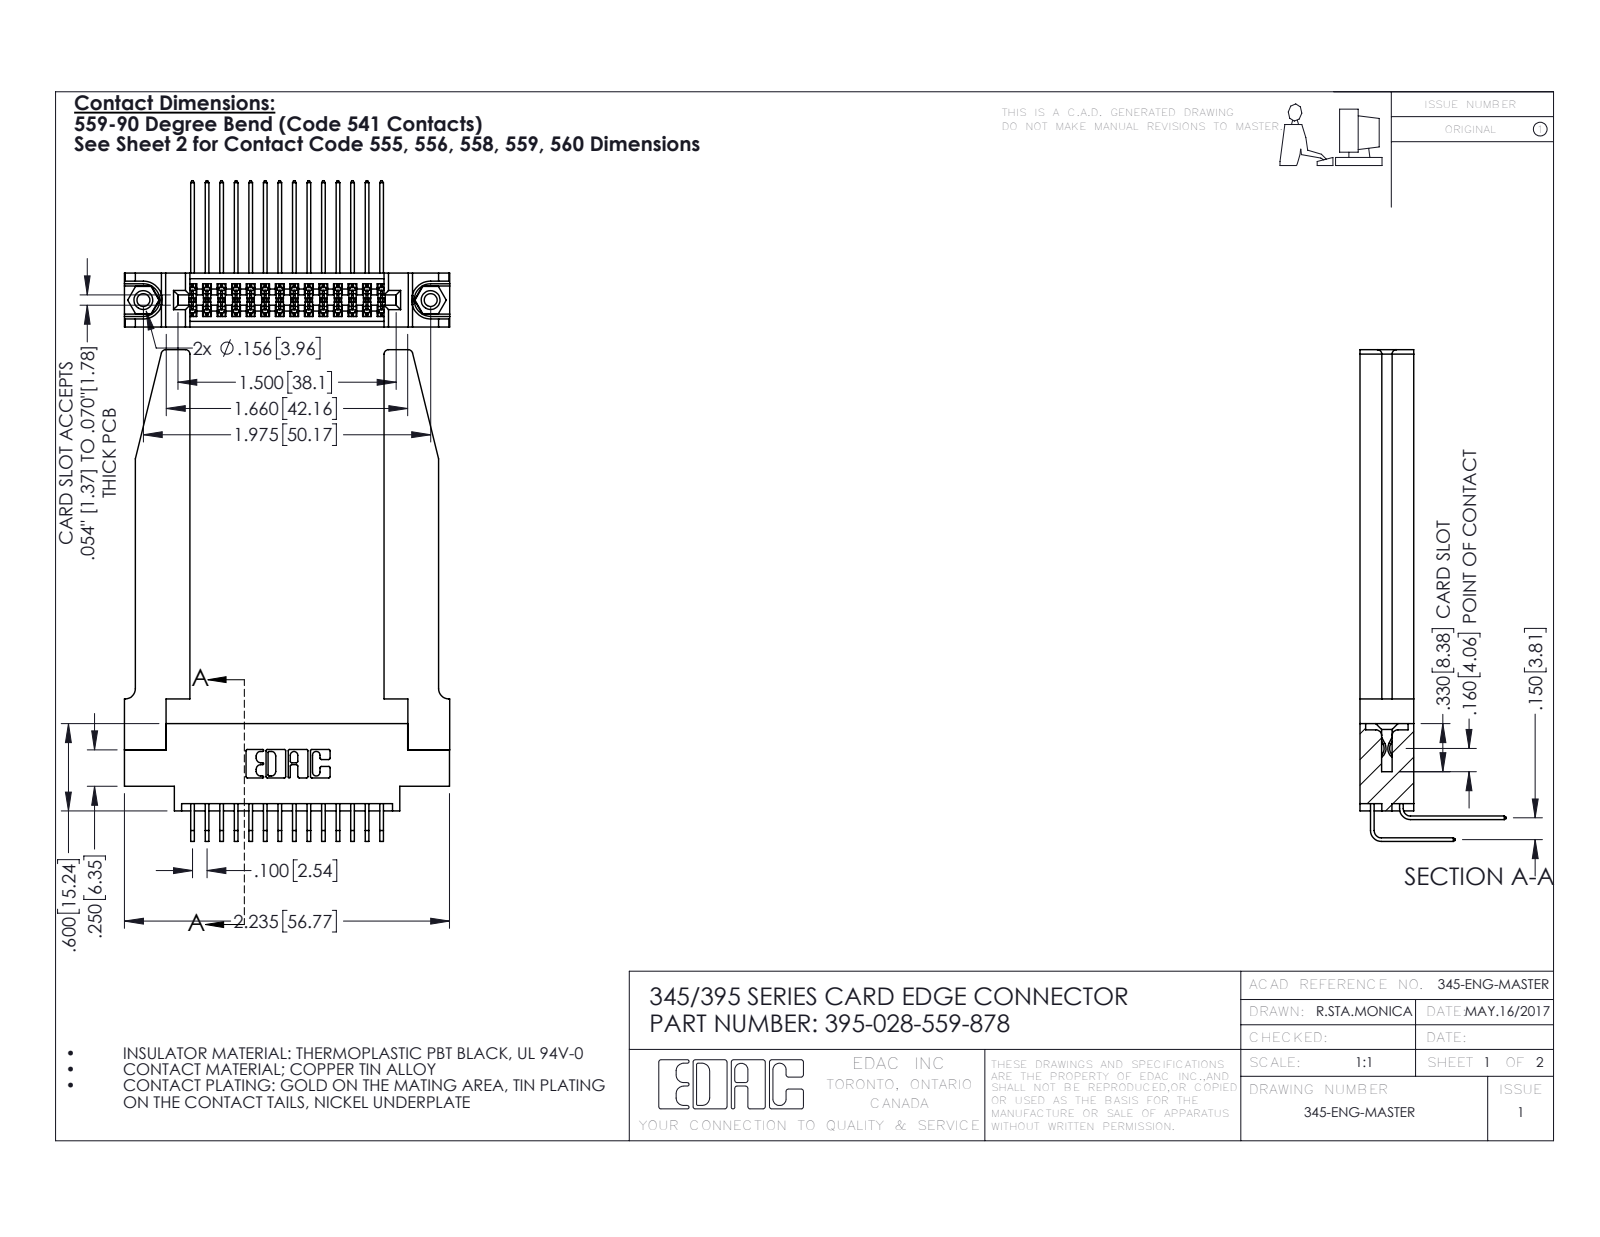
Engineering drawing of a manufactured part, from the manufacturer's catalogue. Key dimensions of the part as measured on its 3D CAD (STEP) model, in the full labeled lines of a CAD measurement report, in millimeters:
Part name (STEP PRODUCT): 345-250-001_345-250-001-102; 345-292-001_559 Tail - 2; 345-220-078_345-220-078; 345 Part_0.170 Offset - 0.156 Dia-TH (+2 more)
STEP written by: SolidWorks 2016 (CONFIG_CONTROL_DESIGN)
Units: millimetres
Bodies: 33 solids, 1820 faces (1206 planar, 562 cylindrical, 52 other)
Overall size (bounding box): 85.8 × 56.8 × 25.5
Volume: 13 100 mm³ · Surface area: 15 040 mm²
Round holes (diameter × count): ⌀2.3 ×2, ⌀3.2 ×2, ⌀4 ×2, ⌀1.6 ×1
Round bosses / shafts (diameter × count): ⌀3.9 ×2
Partial cylindrical surfaces — rounded edges, fillets, slot ends (radius × count): R0.2 ×42, R0.3 ×22, R0.8 ×8, R0.2 ×6, R0.8 ×6, R0.7 ×3, R0.4 ×2, R0.5 ×2
Main face-to-face distances: 9.4, 1.8, 7.6, 3.8, 3.8, 5.1, 5.6, 2, 2.5, 6.9
Hole centre spacings: 6.9, 44.2, 50.2
